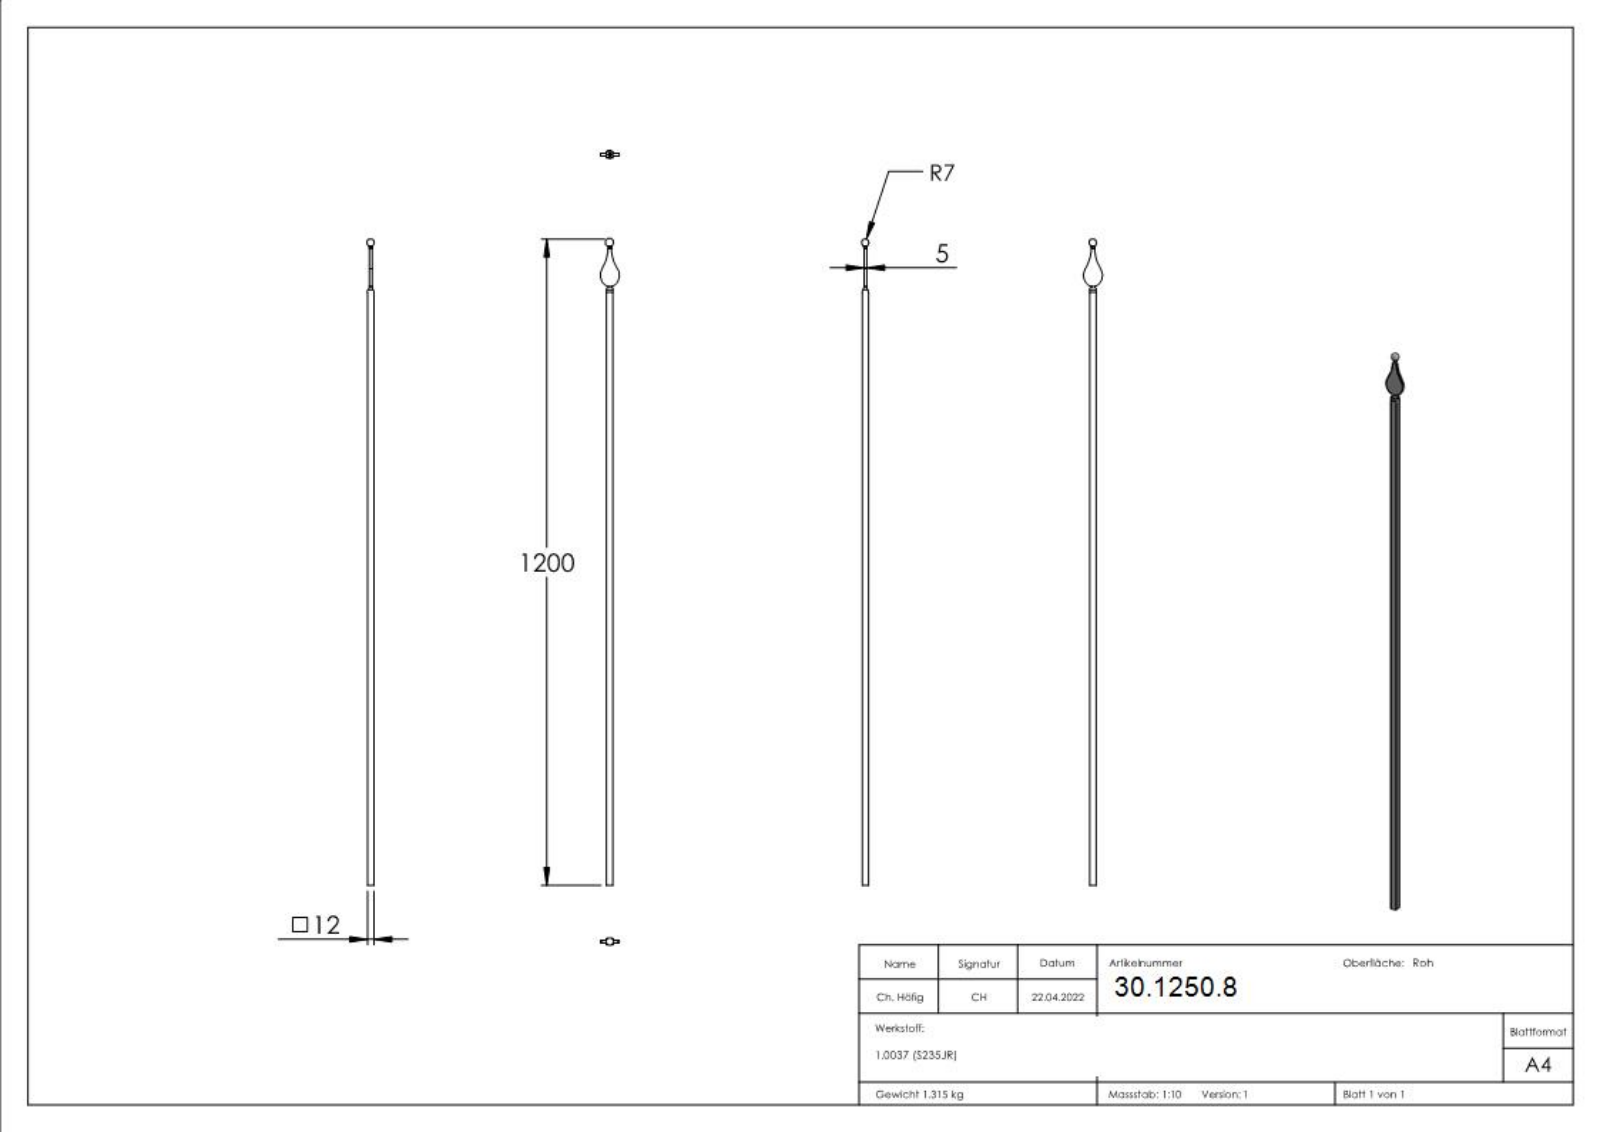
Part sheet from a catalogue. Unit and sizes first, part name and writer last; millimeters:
Units: millimetres
Overall size (bounding box): 1200 × 35 × 14
Partial cylindrical surfaces — rounded edges, fillets, slot ends (radius × count): R7.35 ×2, R8 ×2, R10 ×2, R79.94 ×2
Main face-to-face distances: 12, 8.5, 3.5, 5, 3, 9, 6, 1.76, 0.92, 2.32
Volume: 168 593 mm³ · Surface area: 57 894 mm²
Bodies: 1 solid, 253 faces (124 planar, 8 cylindrical, 121 other)
Part name (STEP PRODUCT): 18518
STEP written by: SolidWorks 2018 (CONFIG_CONTROL_DESIGN)
